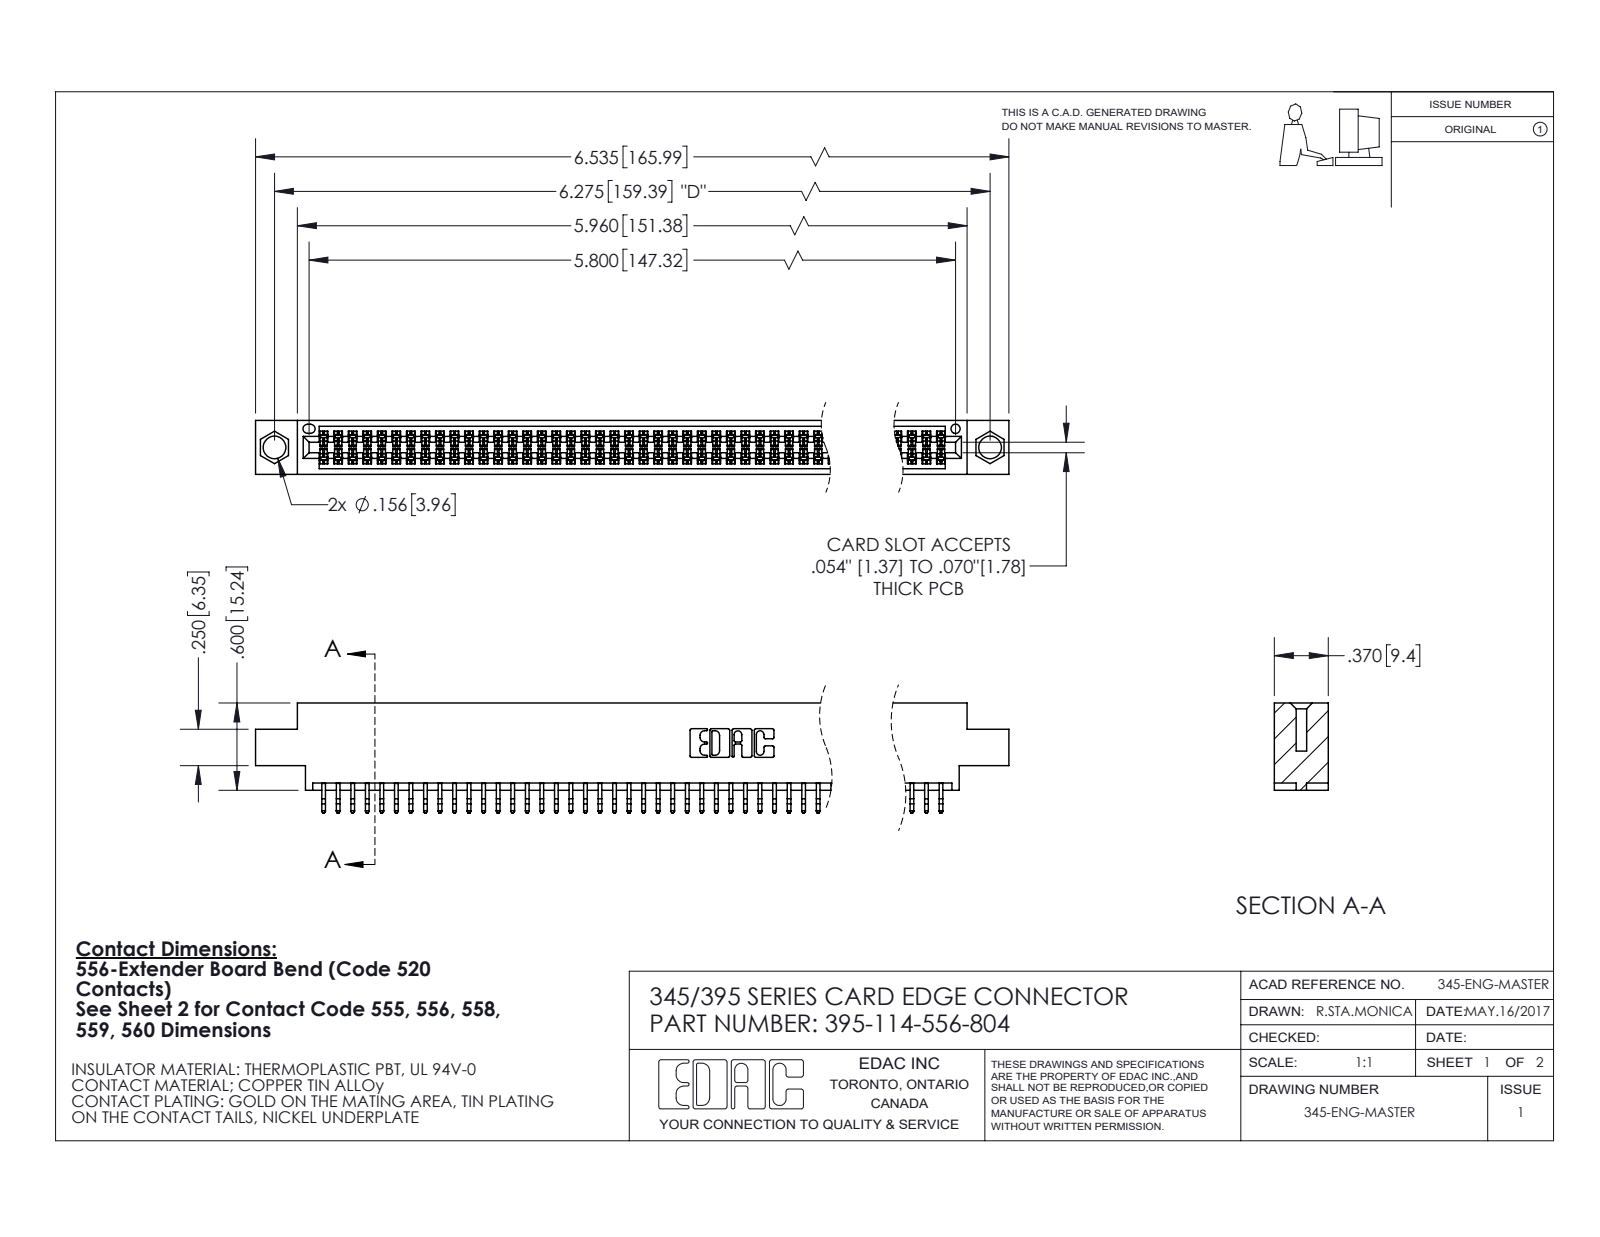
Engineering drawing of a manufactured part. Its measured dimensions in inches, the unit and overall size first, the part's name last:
Units: inches
Overall size (bounding box): 6.535 × 0.757 × 0.37
Round holes (diameter × count): ⌀0.156 ×2, ⌀0.064 ×1
Partial cylindrical surfaces — rounded edges, fillets, slot ends (radius × count): R0.006 ×228, R0.01 ×22, R0.007 ×6, R0.031 ×6, R0.026 ×3, R0.01 ×2, R0.014 ×2, R0.019 ×2
Main face-to-face distances: 0.072, 0.298, 0.37, 0.025, 0.2, 0.098, 0.272, 0.225, 0.175, 0.149
Hole centre spacings: 0.27, 6.039, 6.275
Volume: 0.979 in³ · Surface area: 37.04 in²
Bodies: 115 solids, 6528 faces (4316 planar, 2212 cylindrical, 0 other)
Part name (STEP PRODUCT): 395-114-556-804; 345 Part_0.170 Offset - 0.156 Dia-TI; 345-292-001_556 Tail
STEP written by: SolidWorks 2020 (CONFIG_CONTROL_DESIGN)
